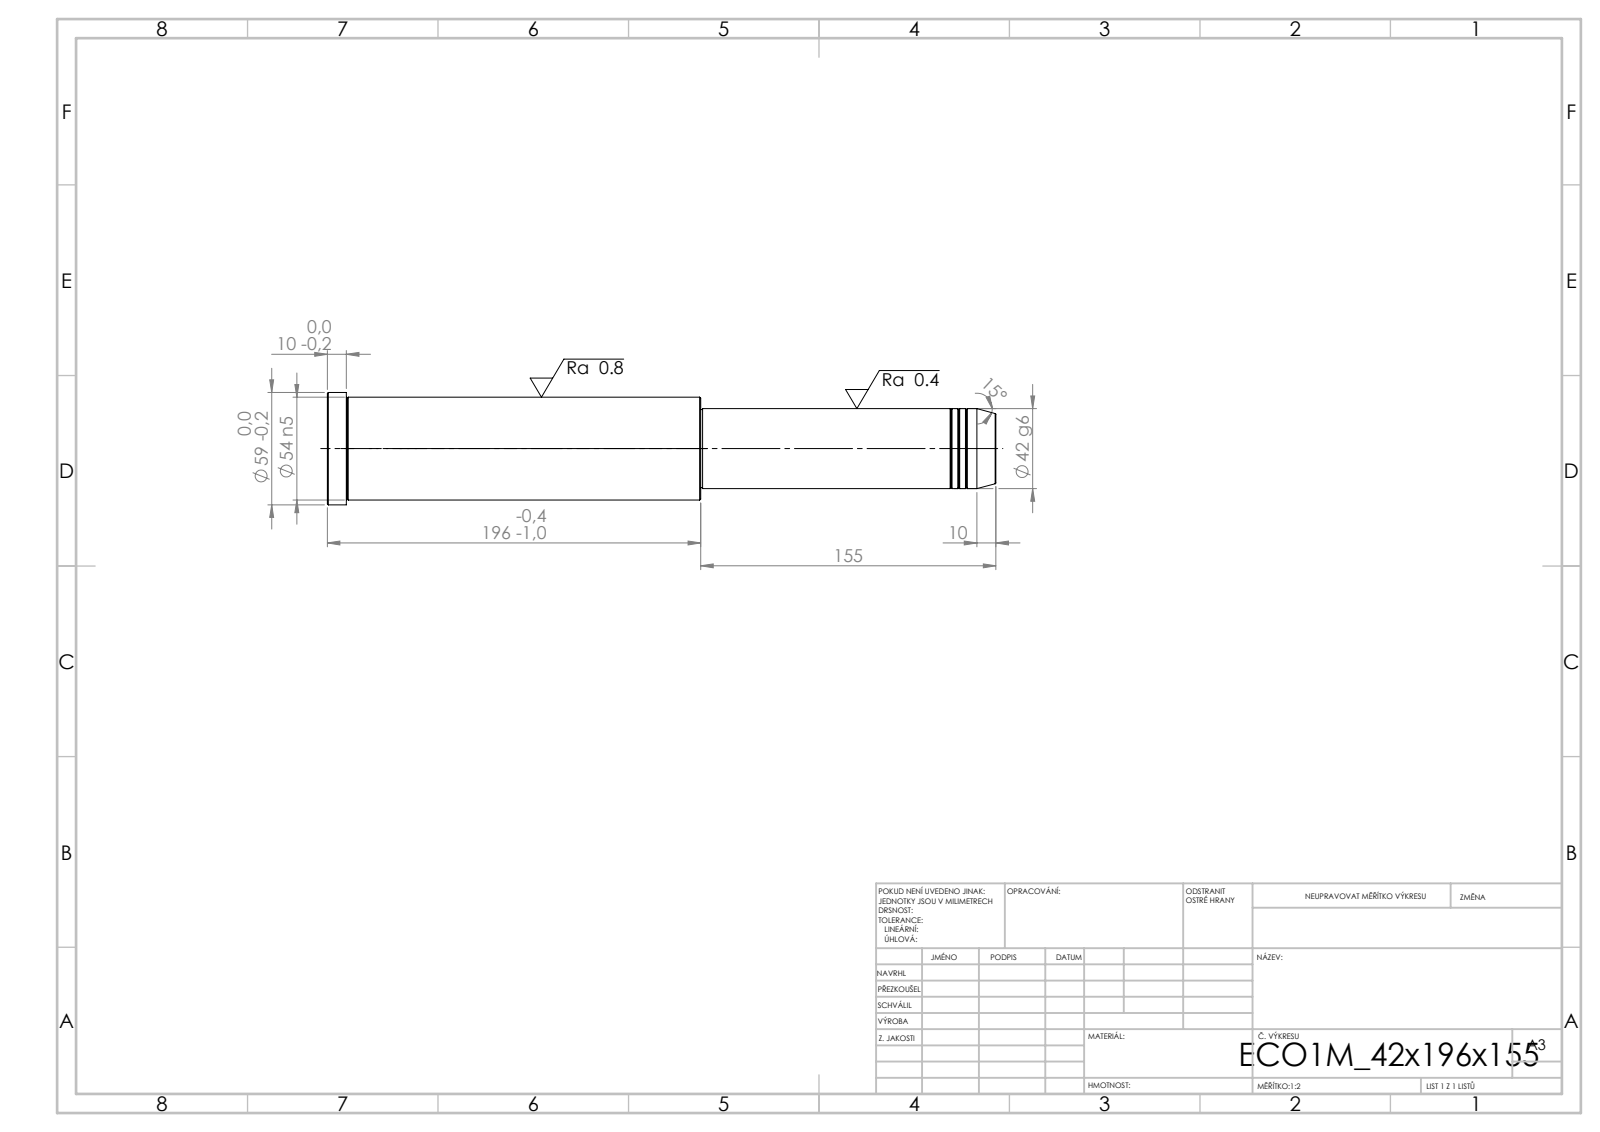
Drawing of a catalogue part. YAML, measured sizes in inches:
step_written_by: "SolidWorks 2019 (CONFIG_CONTROL_DESIGN)"
units: inches
bodies: {solids: 1, faces: 43, planar: 5, cylindrical: 14, other: 24}
overall_size: [13.819, 2.323, 2.323]
volume: 40.64
surface_area: 91.88
round_bosses_or_shafts:
  - {diameter: 2.323, count: 1}
  - {diameter: 2.126, count: 1}
  - {diameter: 1.654, count: 1}
  - {diameter: 1.614, count: 1}
face_to_face_distances: [13.819, 6.102, 7.717, 13.425, 7.323, 0.394, 6.063, 0.039, 7.362, 7.756]
